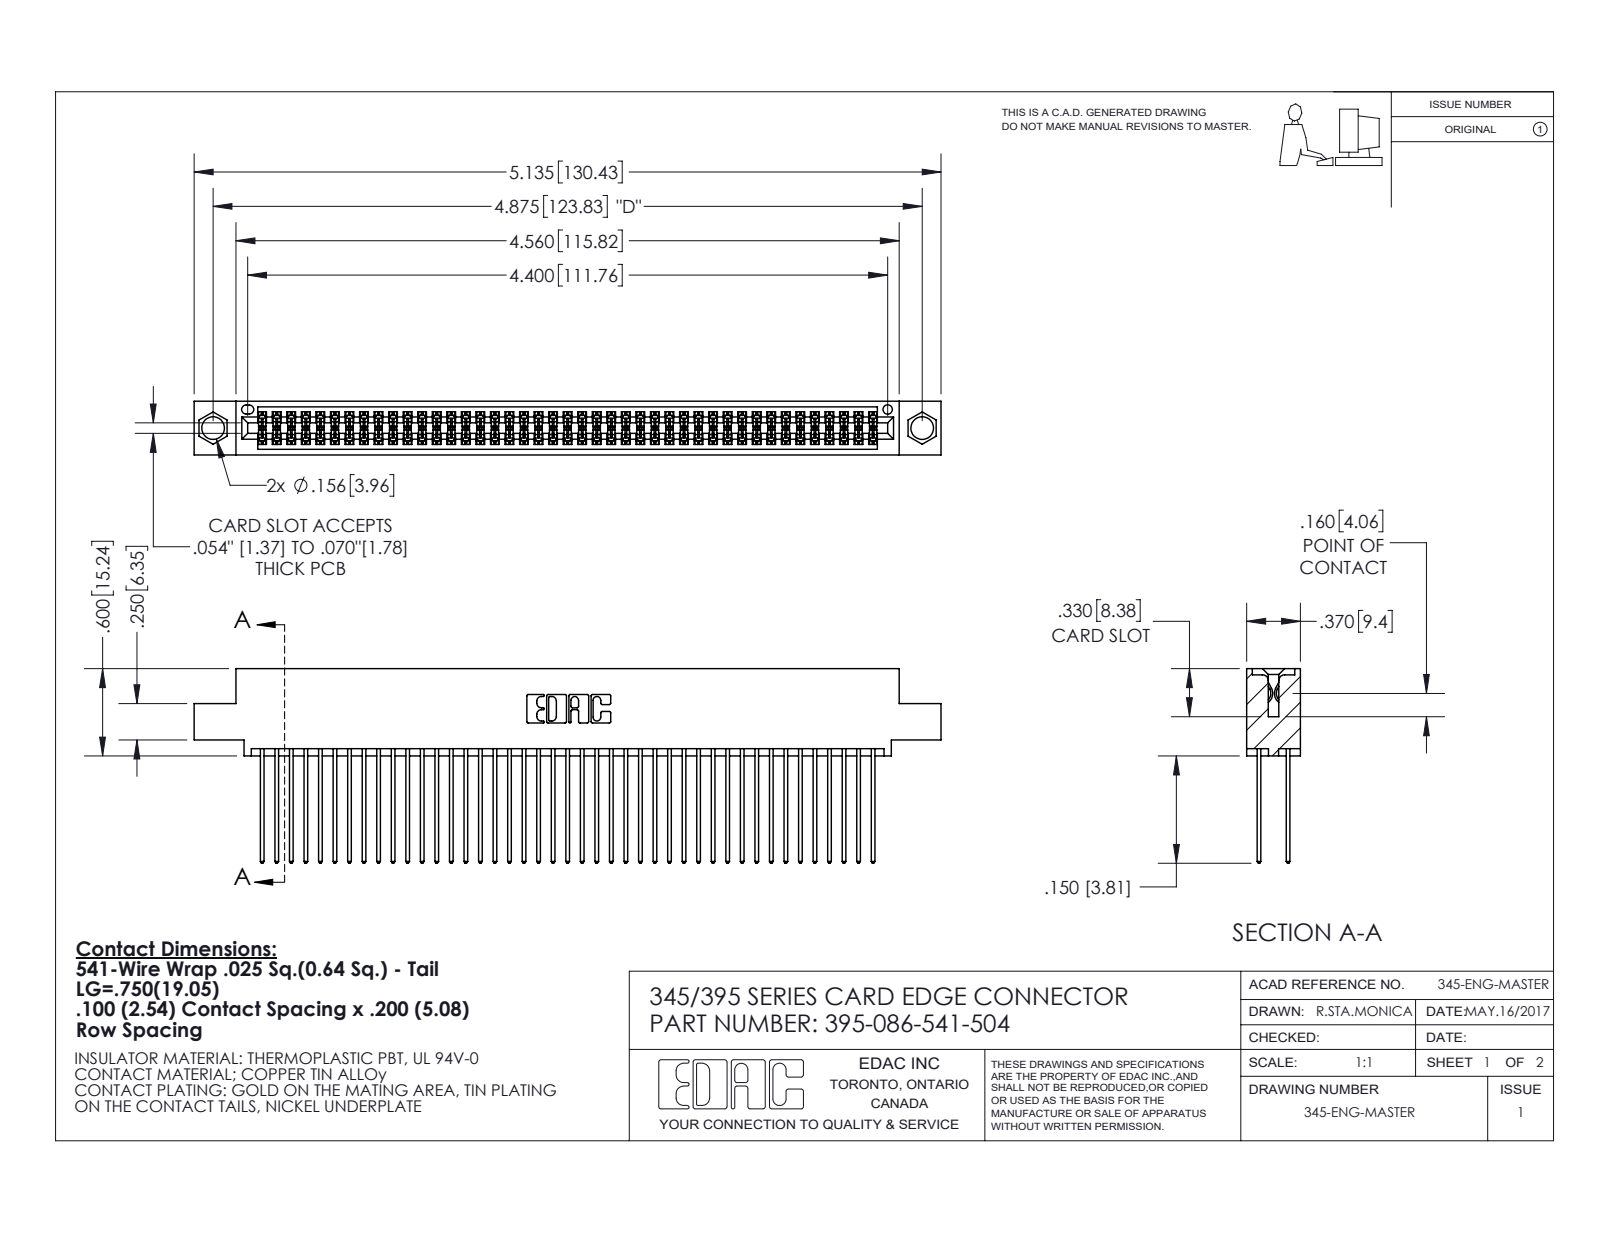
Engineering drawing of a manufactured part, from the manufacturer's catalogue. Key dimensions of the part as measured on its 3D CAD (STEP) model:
Part name (STEP PRODUCT): 345-292-001_345-293-141; 395-086-541-504; 345 Part_0.110 Offset - 0.156 Dia-TI
STEP written by: SolidWorks 2020 (CONFIG_CONTROL_DESIGN)
Units: inches
Bodies: 87 solids, 4444 faces (2936 planar, 1508 cylindrical, 0 other)
Overall size (bounding box): 5.135 × 1.337 × 0.37
Volume: 0.793 in³ · Surface area: 33.31 in²
Round holes (diameter × count): ⌀0.156 ×2, ⌀0.064 ×1
Partial cylindrical surfaces — rounded edges, fillets, slot ends (radius × count): R0.006 ×129, R0.01 ×86, R0.01 ×22, R0.007 ×6, R0.031 ×6, R0.026 ×3, R0.014 ×2, R0.019 ×2
Main face-to-face distances: 0.072, 0.298, 0.2, 0.098, 0.272, 0.025, 0.225, 0.37, 0.175, 0.149
Hole centre spacings: 0.27, 4.639, 4.875
